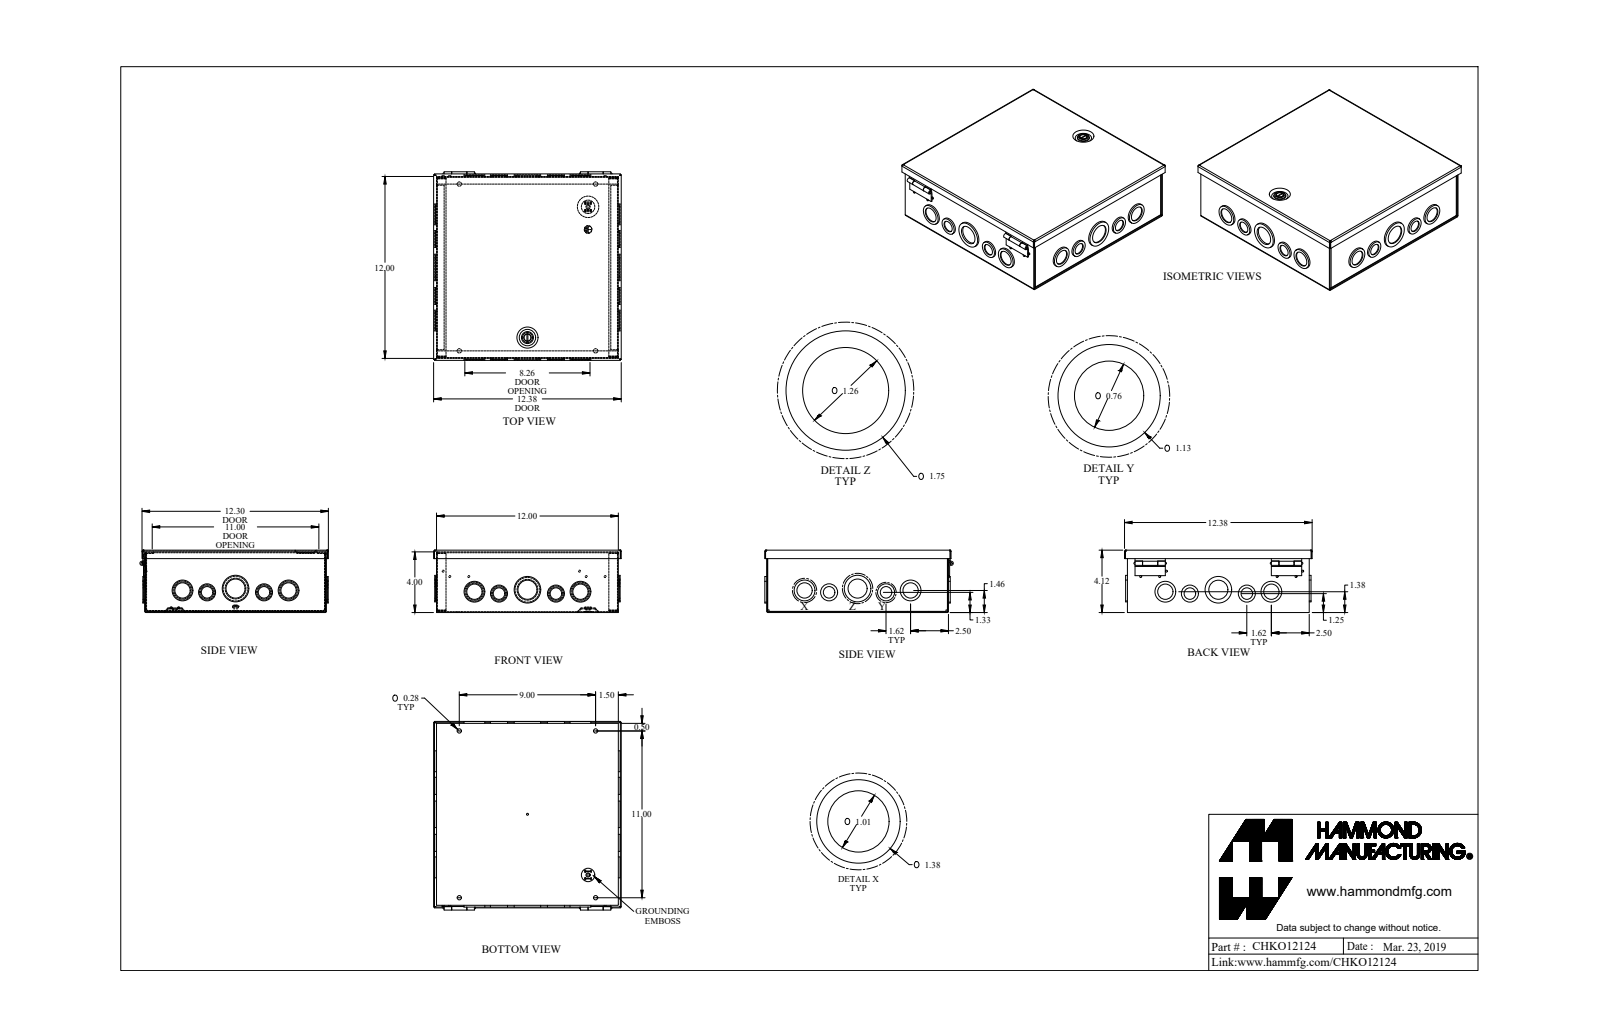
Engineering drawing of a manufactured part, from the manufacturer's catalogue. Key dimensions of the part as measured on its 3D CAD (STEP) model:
Part name (STEP PRODUCT): CHKO12124_Default
STEP written by: SolidWorks 2019 (CONFIG_CONTROL_DESIGN)
Units: inches
Bodies: 12 solids, 727 faces (352 planar, 332 cylindrical, 43 other)
Overall size (bounding box): 12.443 × 12.38 × 4.118
Volume: 32.92 in³ · Surface area: 1 160 in²
Round holes (diameter × count): ⌀1.011 ×8, ⌀1.261 ×6, ⌀0.281 ×4, ⌀0.761 ×4, ⌀1.636 ×2, ⌀0.125 ×1, ⌀0.17 ×1, ⌀0.319 ×1, ⌀0.476 ×1, ⌀0.5 ×1
Round bosses / shafts (diameter × count): ⌀0.131 ×8, ⌀1.125 ×6, ⌀1.375 ×5, ⌀0.875 ×4, ⌀1.375 ×3, ⌀1.75 ×2, ⌀1.125 ×2, ⌀0.875 ×2
Partial cylindrical surfaces — rounded edges, fillets, slot ends (radius × count): R0.029 ×16, R0.086 ×16, R0.057 ×8, R0.012 ×4, R0.1 ×4, R0.036 ×2, R0.079 ×2, R0.25 ×2
Main face-to-face distances: 0.057, 4.061, 11.943, 4.118, 4.004, 12, 11.886, 3.943, 0.118, 0.08
Hole centre spacings: 1.625, 1.896, 3.502, 5.381, 3.76, 7, 9, 11
